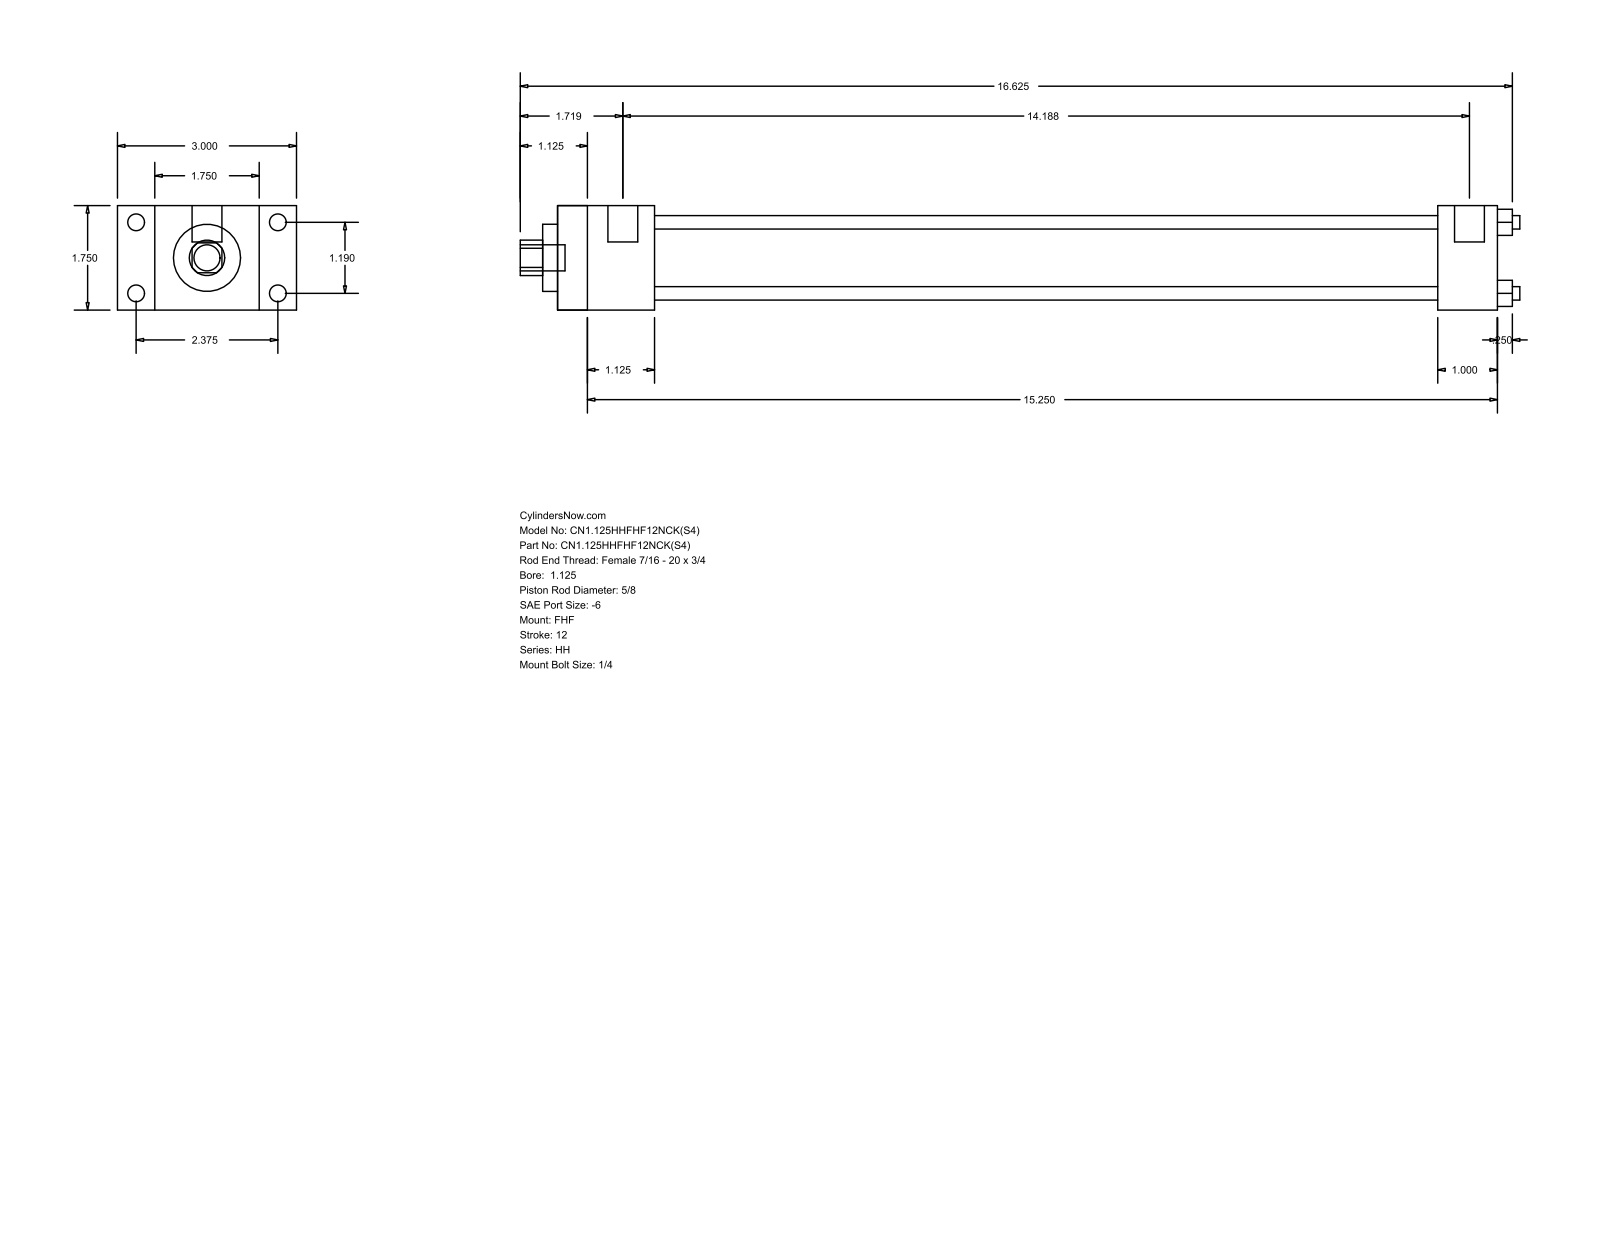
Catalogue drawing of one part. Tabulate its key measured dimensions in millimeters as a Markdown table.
| quantity | value |
| --- | --- |
| part name | HH_FHF__0112_0.625 |
| STEP written by | GSSL Pune (CONFIG_CONTROL_DESIGN) |
| units | millimeters |
| bodies | 0 solids, 88 faces (60 planar, 28 cylindrical, 0 other) |
| overall size | 425.45 × 76.2 × 44.45 |
| round holes (diameter × count) | 5.71 × 4, 15.88 × 1, 28.57 × 1, 34.92 × 1 |
| round bosses / shafts (diameter × count) | 7.14 × 4, 5.56 × 4, 12.7 × 2, 11.11 × 1 |
| partial cylindrical surfaces (radius × count) | 7.54 × 1 |
| main face-to-face distances | 44.46, 15.87, 60.33, 41.27, 76.2, 400.05, 358.78, 374.64, 333.37, 25.41 |
| hole center spacings | 21.37, 30.22, 42.74 |
